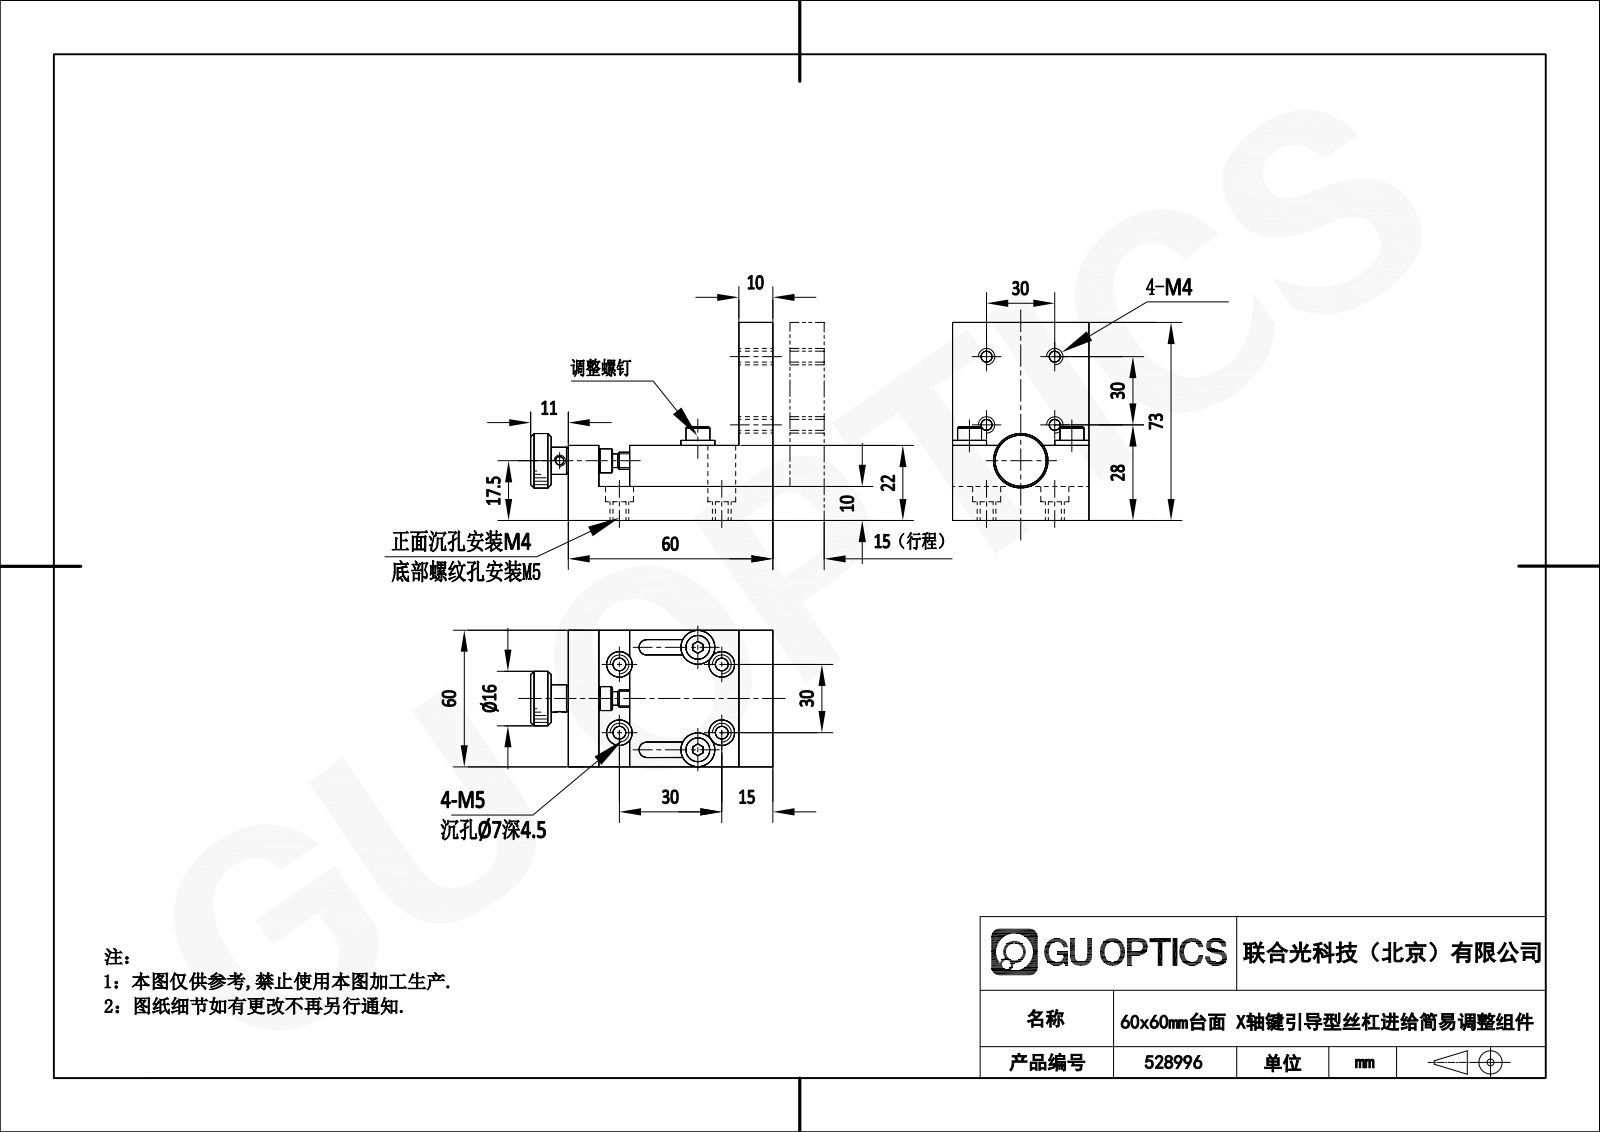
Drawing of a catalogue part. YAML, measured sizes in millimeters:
part_name: "528996"
step_written_by: "SolidWorks 2020 (CONFIG_CONTROL_DESIGN)"
units: millimeters
bodies: {solids: 5, faces: 372, planar: 162, cylindrical: 86, other: 124}
overall_size: [73, 71, 60]
volume: 99748
surface_area: 31742
round_holes:
  - {diameter: 3.24, count: 6}
  - {diameter: 4.13, count: 5}
  - {diameter: 7.5, count: 4}
  - {diameter: 2.46, count: 1}
  - {diameter: 4.5, count: 1}
  - {diameter: 5.5, count: 1}
round_bosses_or_shafts:
  - {diameter: 7, count: 3}
  - {diameter: 5, count: 3}
  - {diameter: 10, count: 2}
  - {diameter: 8, count: 1}
  - {diameter: 4, count: 1}
partial_cylinders:
  - {radius: 2.25, count: 4}
  - {radius: 1, count: 1}
  - {radius: 8, count: 1}
face_to_face_distances: [10, 60, 22, 12, 41, 50, 51, 9, 31, 19]
hole_center_spacings: [30, 42.43, 10.3, 18.31, 26.57, 39.32, 43.19, 46.32]
